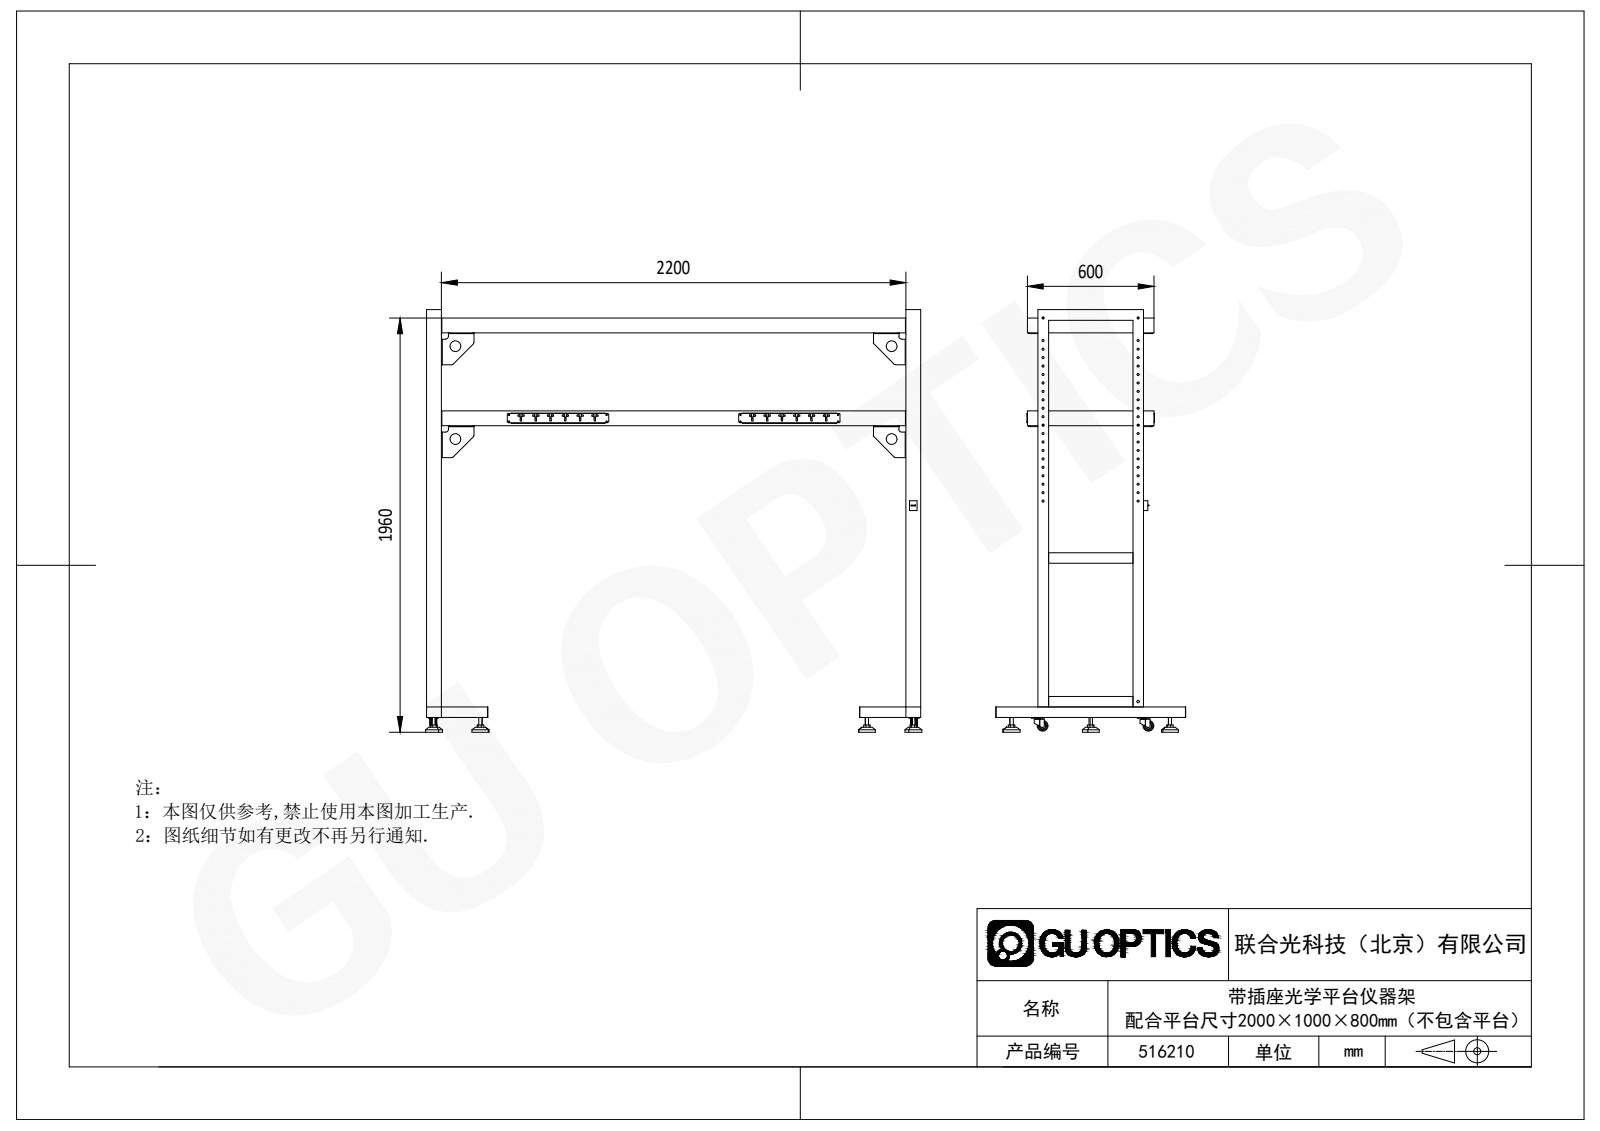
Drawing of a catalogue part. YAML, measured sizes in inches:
part_name: "516210"
step_written_by: "SolidWorks 2020 (CONFIG_CONTROL_DESIGN)"
units: inches
bodies: {solids: 59, faces: 2591, planar: 1443, cylindrical: 1072, other: 76}
overall_size: [92.52, 78.78, 35.433]
volume: 1436
surface_area: 25900
round_holes:
  - {diameter: 0.354, count: 66}
  - {diameter: 0.24, count: 16}
  - {diameter: 0.394, count: 16}
  - {diameter: 0.256, count: 12}
  - {diameter: 0.165, count: 8}
  - {diameter: 0.205, count: 8}
  - {diameter: 0.236, count: 8}
  - {diameter: 0.669, count: 6}
  - {diameter: 0.709, count: 6}
  - {diameter: 1.024, count: 6}
  - {diameter: 2.717, count: 6}
  - {diameter: 0.126, count: 4}
round_bosses_or_shafts:
  - {diameter: 3.15, count: 6}
  - {diameter: 0.63, count: 6}
  - {diameter: 1.024, count: 4}
  - {diameter: 0.709, count: 4}
  - {diameter: 1.969, count: 2}
  - {diameter: 0.394, count: 2}
partial_cylinders:
  - {radius: 0.197, count: 36}
  - {radius: 0.276, count: 24}
  - {radius: 0.118, count: 16}
  - {radius: 0.167, count: 12}
  - {radius: 0.059, count: 8}
  - {radius: 0.059, count: 8}
  - {radius: 0.158, count: 8}
  - {radius: 0.512, count: 4}
face_to_face_distances: [17.323, 0.059, 0.118, 2.756, 0.079, 1.969, 2.638, 0.098, 17.264, 2.657]
hole_center_spacings: [1.575, 3.15, 4.724, 11.024, 6.299, 7.874, 9.449, 12.598]
